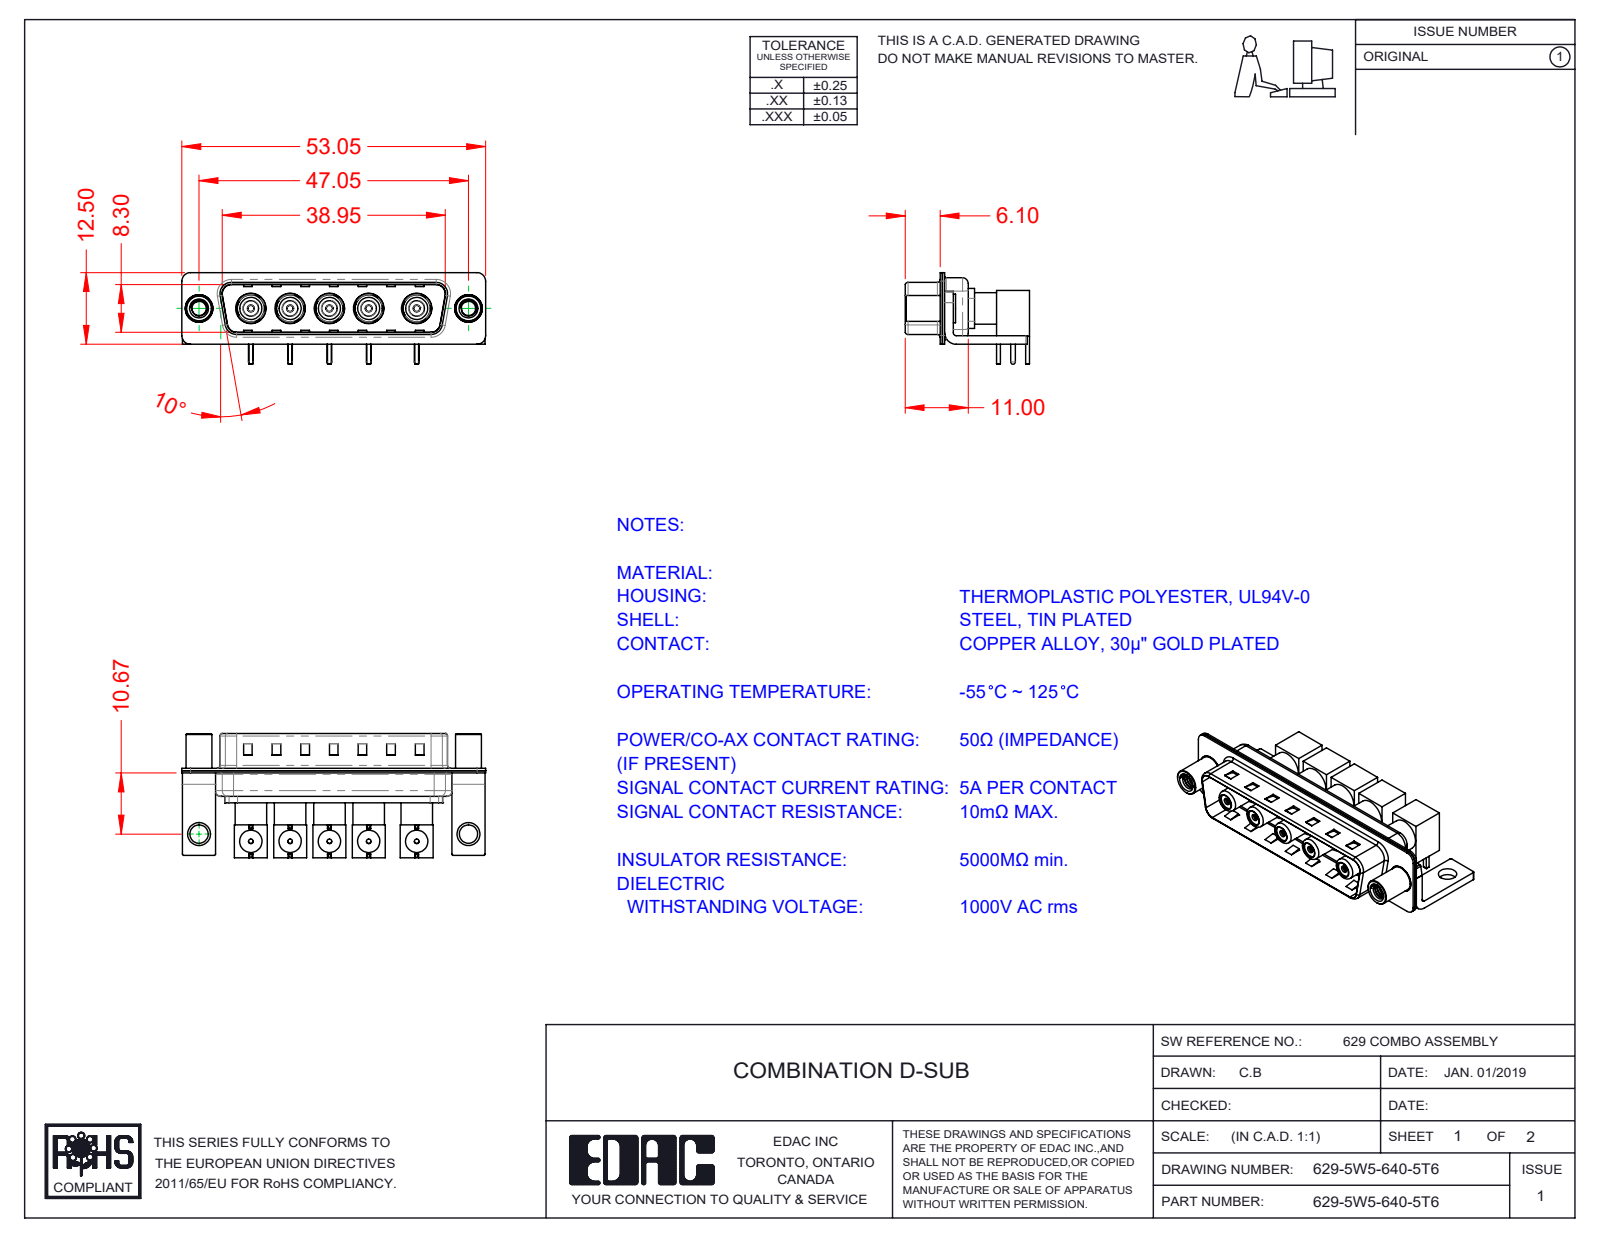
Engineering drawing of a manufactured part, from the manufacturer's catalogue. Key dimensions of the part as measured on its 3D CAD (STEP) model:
Part name (STEP PRODUCT): Co-Ax Jack Assy_RA; Insulator Socket 2; 629Combo Housing_5W5; 629Combo Threaded Standoff_D (+8 more)
STEP written by: SolidWorks 2020 (CONFIG_CONTROL_DESIGN)
Units: millimetres
Bodies: 42 solids, 1234 faces (478 planar, 544 cylindrical, 212 other)
Overall size (bounding box): 53.05 × 21.71 × 16
Volume: 4 527 mm³ · Surface area: 12 293 mm²
Round holes (diameter × count): ⌀2.5 ×7, ⌀0.8 ×5, ⌀1.1 ×5, ⌀1.2 ×5, ⌀1.5 ×5, ⌀1.6 ×5, ⌀2.7 ×5, ⌀3.1 ×5, ⌀3.4 ×5, ⌀3.9 ×5, ⌀4.1 ×5, ⌀4.85 ×5
Round bosses / shafts (diameter × count): ⌀0.8 ×10, ⌀5.5 ×5, ⌀5.2 ×5, ⌀4.8 ×5, ⌀4.73 ×5, ⌀4.16 ×5, ⌀4 ×5, ⌀3.9 ×5
Partial cylindrical surfaces — rounded edges, fillets, slot ends (radius × count): R0.25 ×16, R1.5 ×16, R2 ×13, R0.5 ×9, R1.6 ×8, R2.1 ×5, R0.6 ×4, R0.65 ×4
Main face-to-face distances: 0.4, 0.8, 5.75, 9.5, 1.5, 1.4, 9.1, 8.7, 9.9, 0.35
Hole centre spacings: 6.86, 13.72, 8.38, 20.58, 22.1, 28.96, 6.87, 13.73
